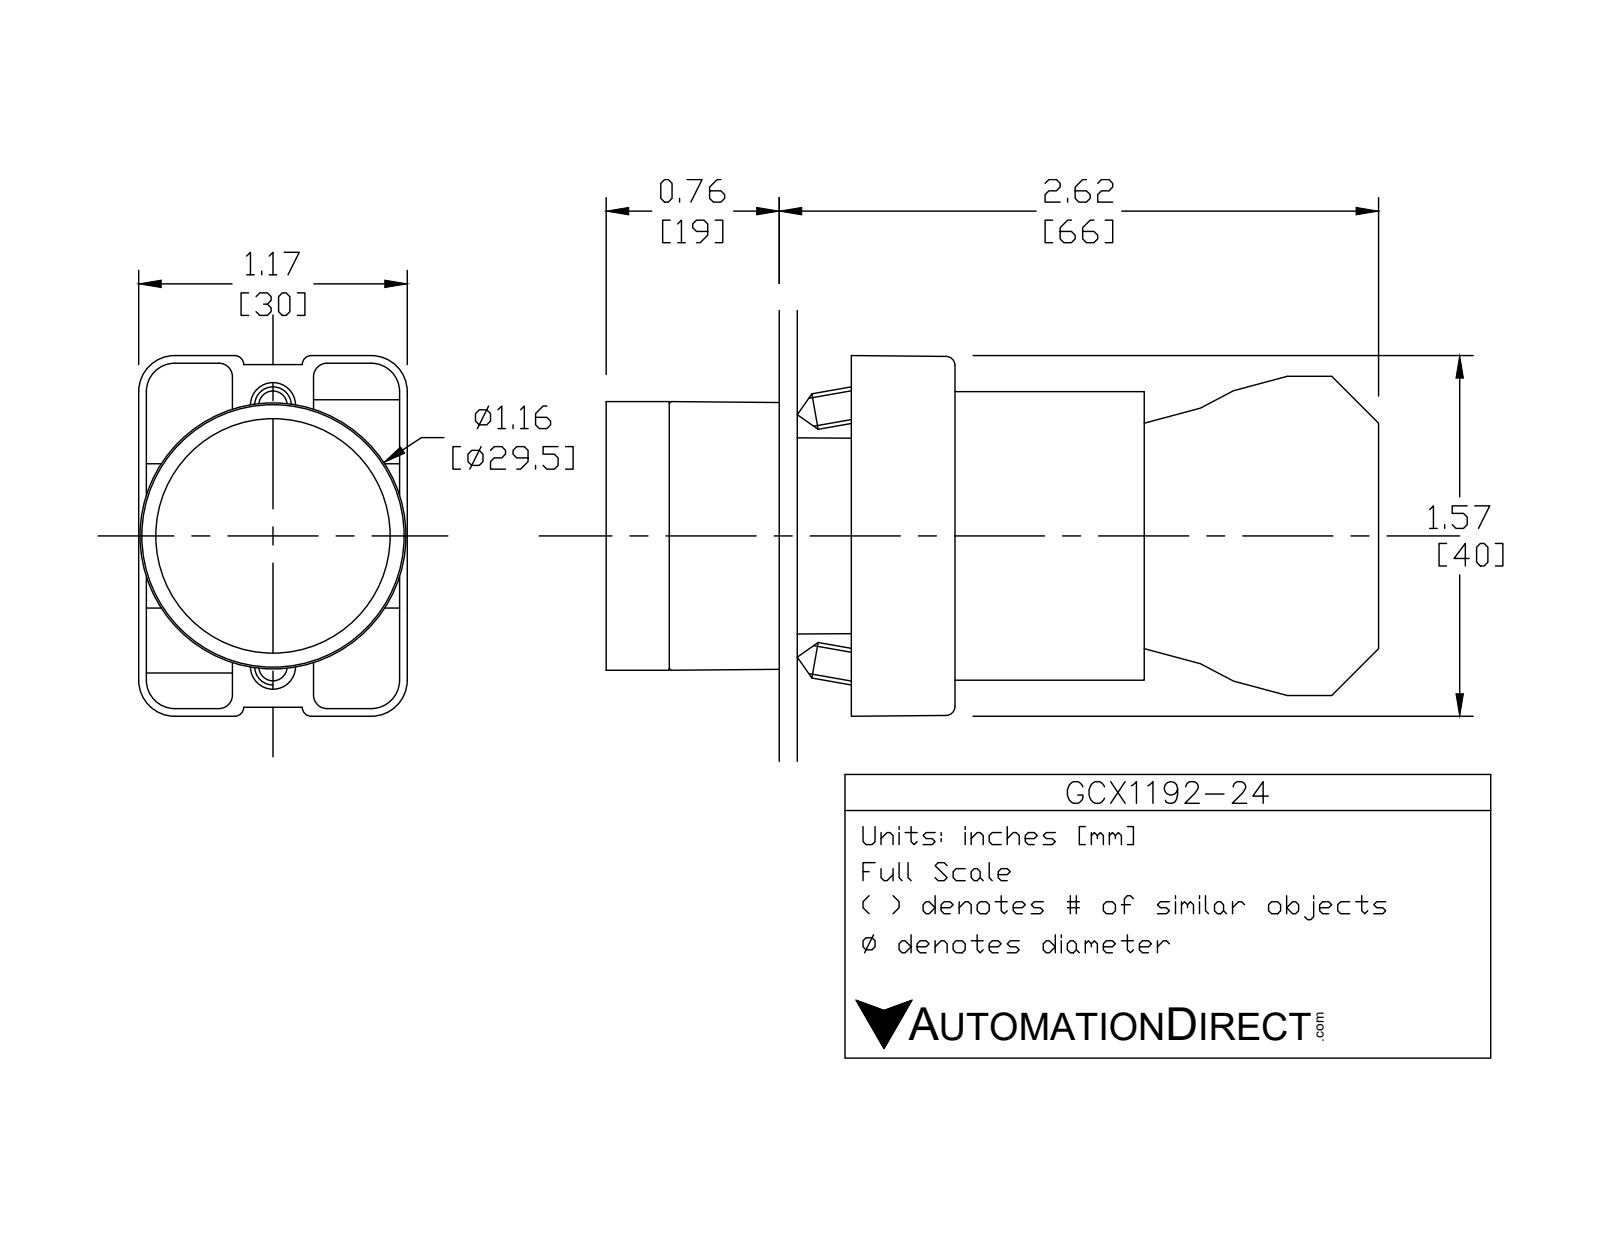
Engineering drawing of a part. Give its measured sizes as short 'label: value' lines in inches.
name: ecx1029; ecx1040; GCX1192-24; GCX1192 OPERATOR (+1 more)
written by: SolidWorks 2016 (AUTOMOTIVE_DESIGN)
unit: in
bodies: 8 solids, 431 faces (252 planar, 148 cylindrical, 31 other)
size: 3.319 × 1.581 × 1.177
volume: 2.794 in³; area: 38.75 in²
holes: 2× ⌀0.079, 2× ⌀0.124, 2× ⌀0.13, 1× ⌀0.087, 1× ⌀0.197, 1× ⌀0.469, 1× ⌀0.878, 1× ⌀0.888, 1× ⌀1.024
bosses: 4× ⌀0.157, 1× ⌀1.175, 1× ⌀1.004, 1× ⌀0.945, 1× ⌀0.856, 1× ⌀0.78, 1× ⌀0.504
rounds: 24× R0.059, 12× R0.041, 12× R0.124, 12× R0.157, 8× R0.039, 2× R0.128, 1× R0.02, 1× R0.063
face distances: 0.827, 2.02, 1.193, 0.579, 1.171, 0.031, 0.276, 0.033, 0.748, 0.573
hole spacings: 0.236, 0.544, 0.472, 0.49
